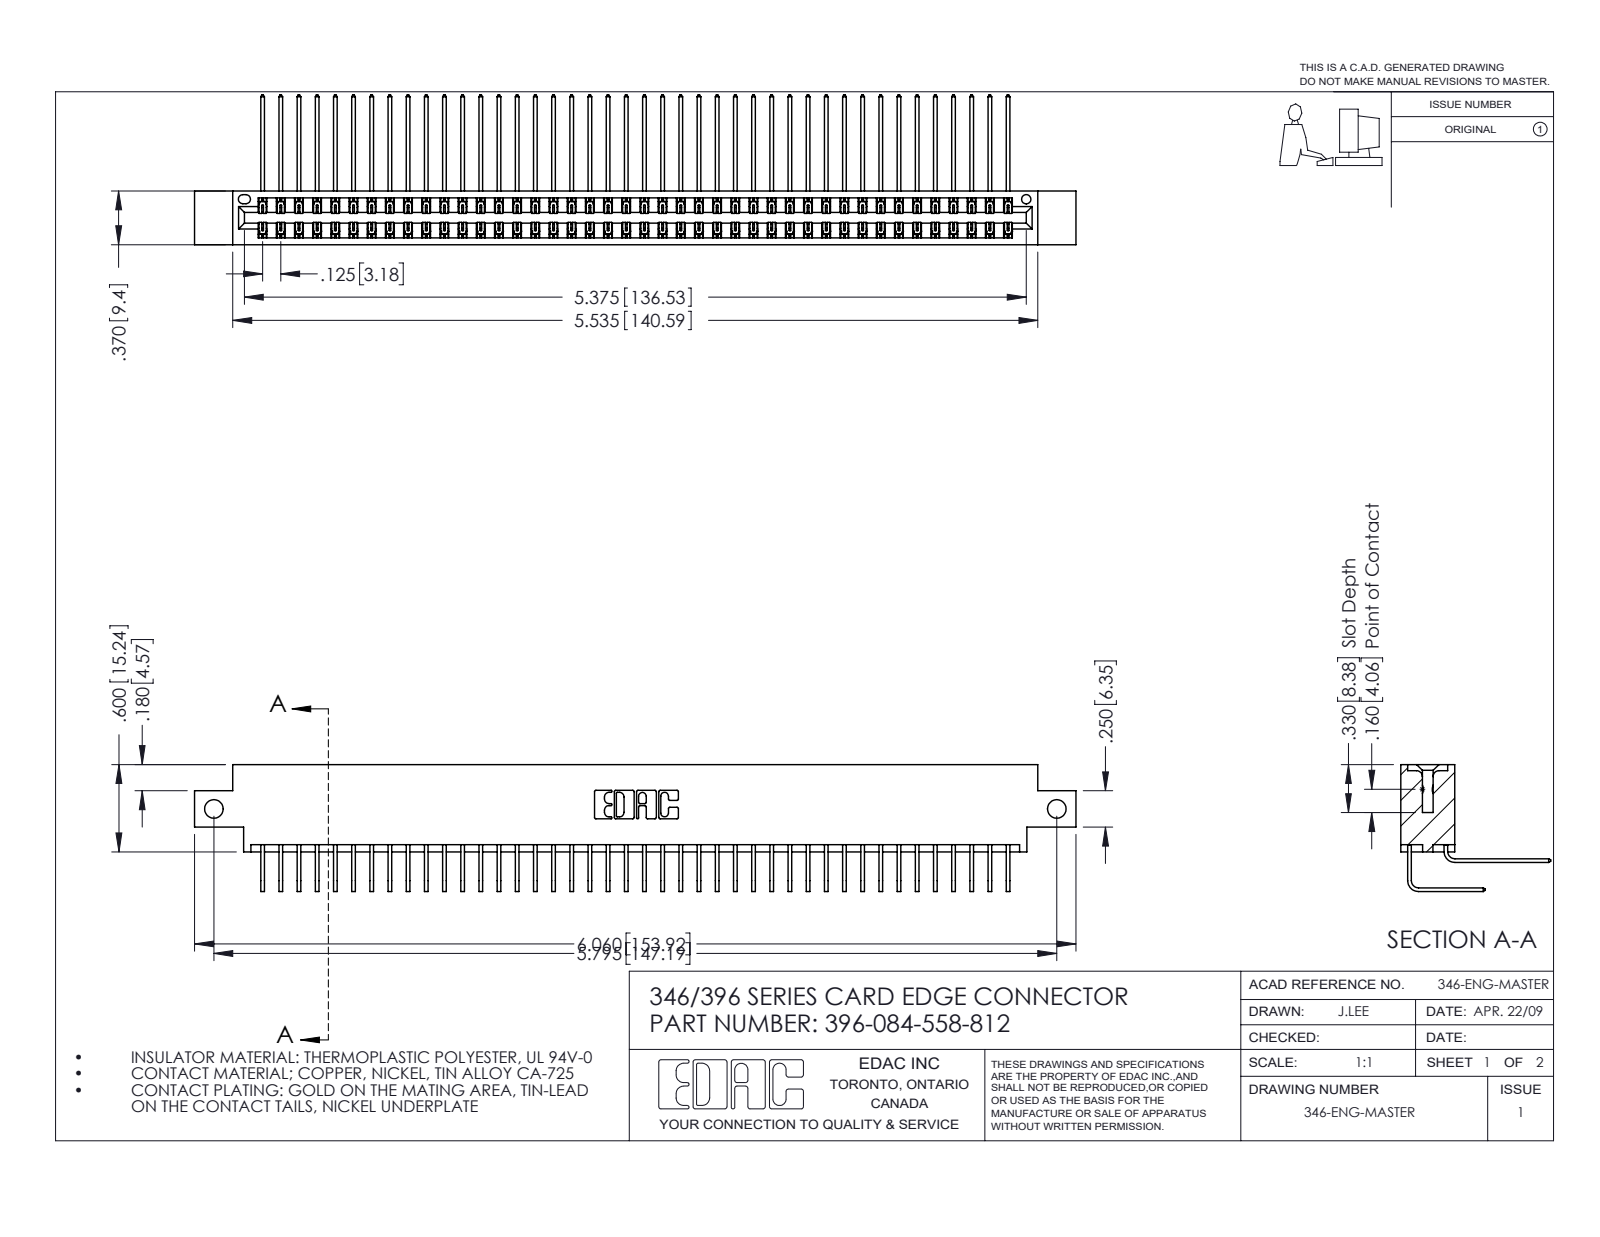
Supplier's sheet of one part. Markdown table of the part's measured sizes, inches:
| quantity | value |
| --- | --- |
| part name | 396-084-558-812; 346 Part_0.170 Offset - Side Mount; 345-292-001_558 559 Tail - 1; 345-292-001_558 Tail - 2 |
| STEP written by | SolidWorks 2016 (CONFIG_CONTROL_DESIGN) |
| units | inches |
| bodies | 85 solids, 4662 faces (3188 planar, 1474 cylindrical, 0 other) |
| overall size | 6.06 × 1.03 × 0.873 |
| volume | 0.931 in³ |
| surface area | 36.16 in² |
| round holes (diameter × count) | 0.128 × 2, 0.064 × 1 |
| partial cylindrical surfaces (radius × count) | 0.006 × 126, 0.01 × 22, 0.007 × 6, 0.031 × 6, 0.026 × 3, 0.014 × 2, 0.022 × 2, 0.024 × 2 |
| main face-to-face distances | 0.322, 0.048, 0.025, 0.37, 0.25, 0.298, 0.072, 0.275, 0.148, 0.222 |
| hole center spacings | 5.795 |
